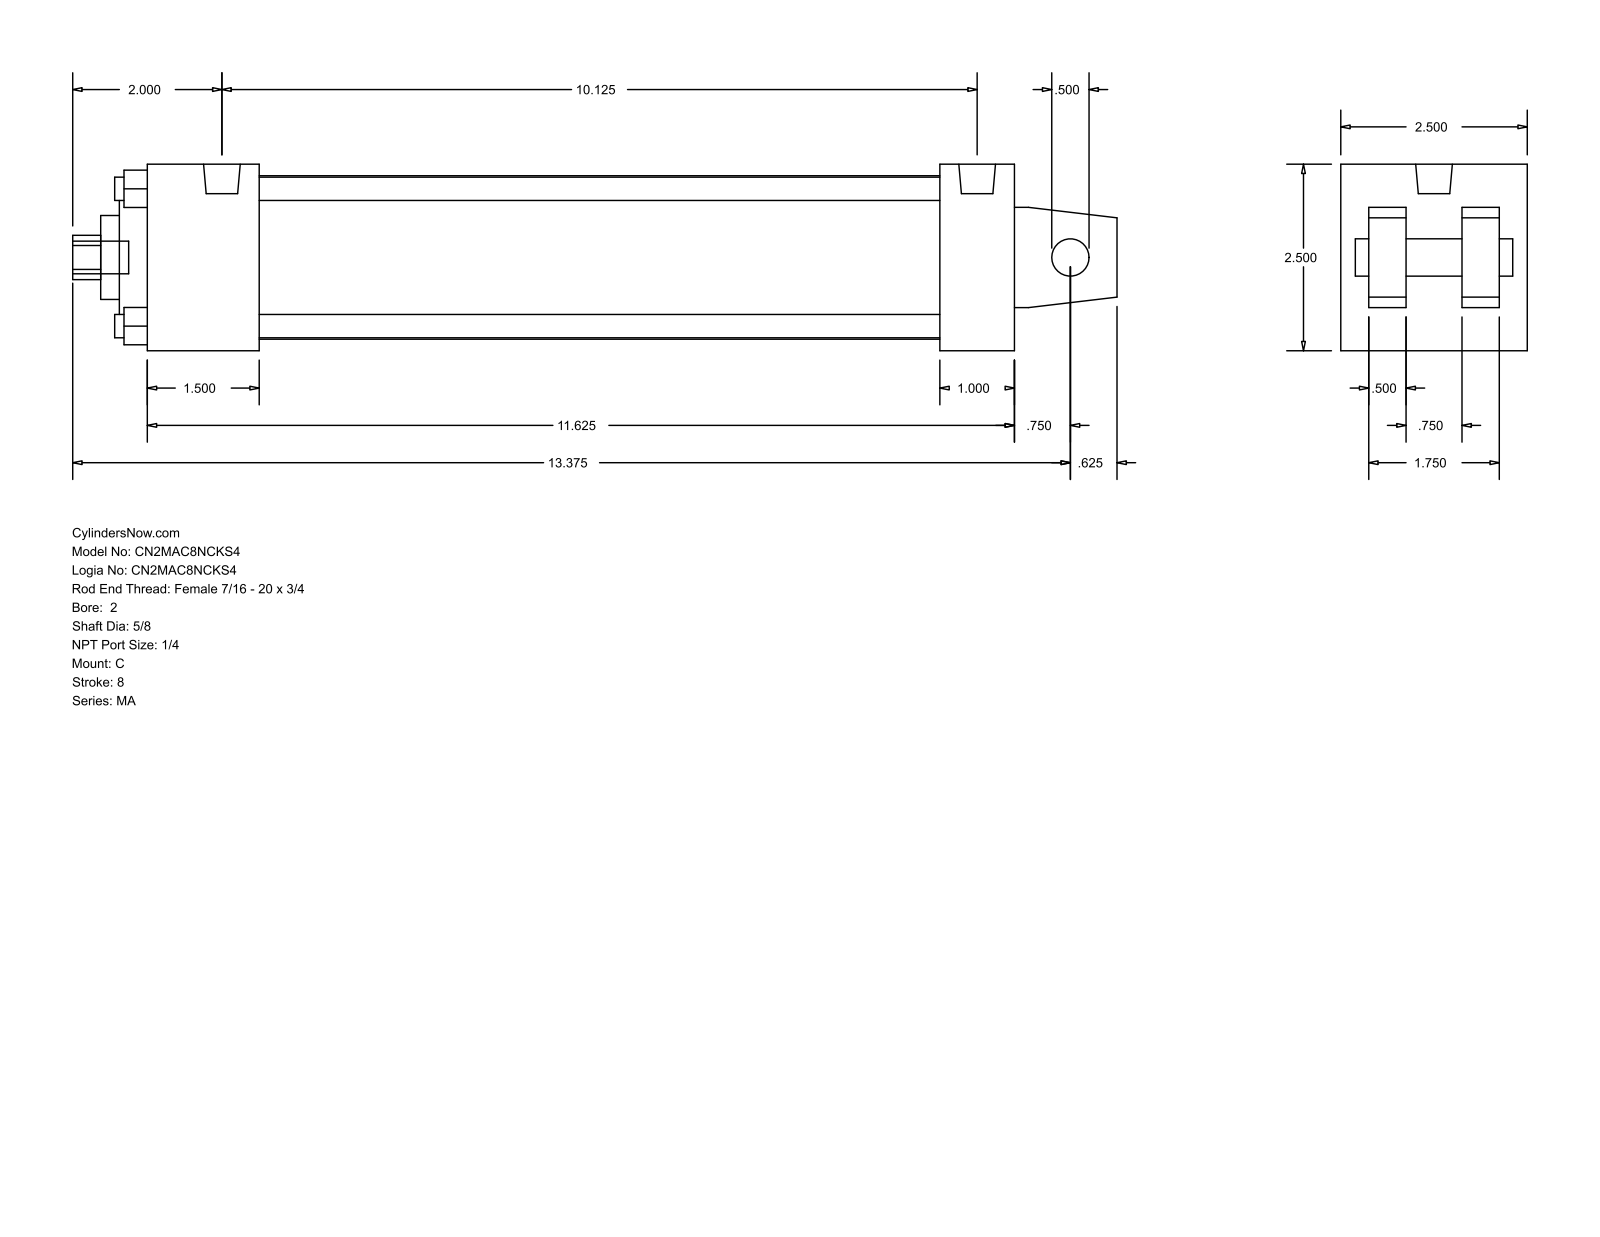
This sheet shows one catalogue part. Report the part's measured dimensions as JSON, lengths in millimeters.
{"part_name": "MA_C__0200_0.625", "step_written_by": "GSSL Pune (CONFIG_CONTROL_DESIGN)", "units": "millimeters", "bodies": {"solids": 0, "faces": 105, "planar": 77, "cylindrical": 28, "other": 0}, "overall_size": [355.6, 63.5, 63.5], "round_holes": [[7.94, 4], [12.7, 1], [15.88, 1], [28.57, 1], [50.8, 1], [55.63, 1]], "round_bosses_or_shafts": [[7.94, 4], [12.49, 2], [11.11, 1]], "partial_cylinders_radius": [[7.54, 1]], "face_to_face_distances": [63.5, 9.52, 12.7, 22.22, 41.28, 53.98, 31.76, 38.1, 295.28, 257.18], "hole_center_spacings": [33.05, 46.74, 66.1]}
